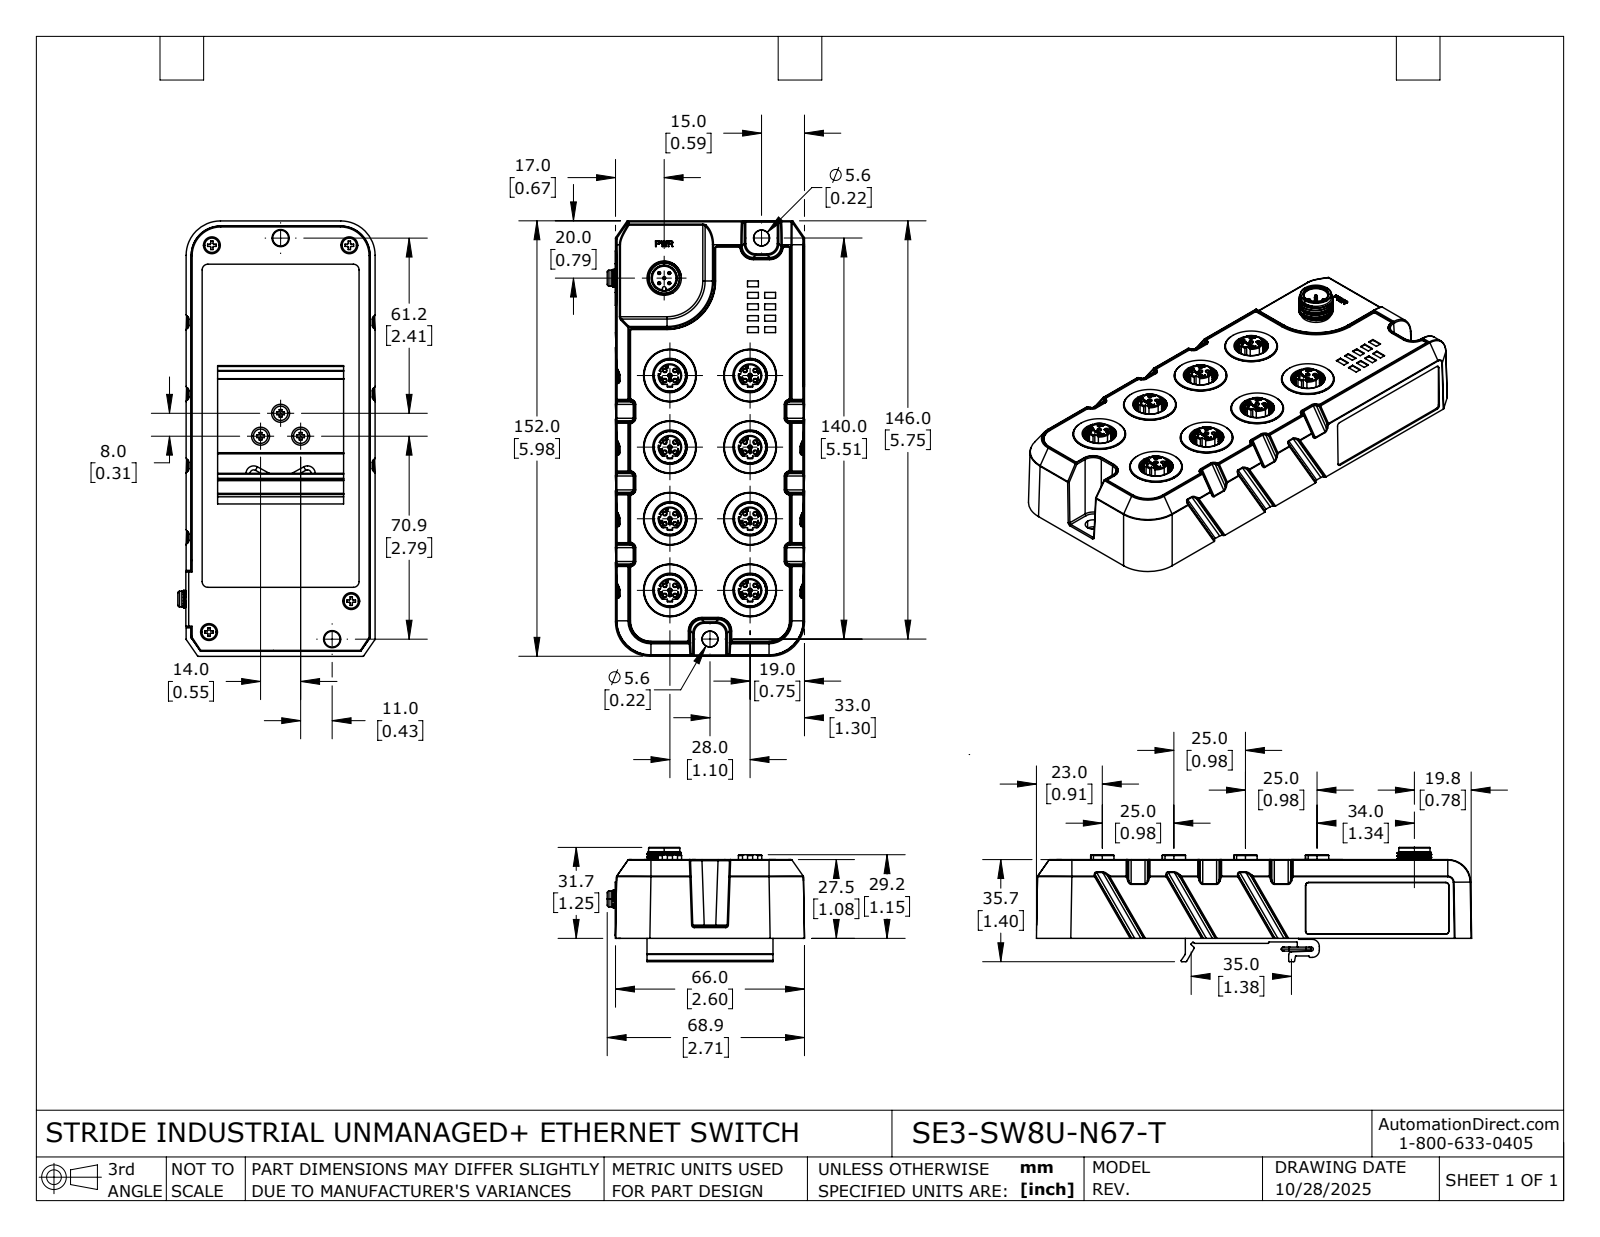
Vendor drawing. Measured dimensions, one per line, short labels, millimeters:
name: SE3-SW8U-N67-T
written by: SolidWorks 2024 (AUTOMOTIVE_DESIGN)
unit: mm
bodies: 9 solids, 4178 faces (2322 planar, 1111 cylindrical, 745 other)
size: 152 × 68.9 × 31.75
volume: 232 624 mm³; area: 78 584 mm²
holes: 40× ⌀1.13, 8× ⌀11, 8× ⌀11.1, 8× ⌀18.2, 4× ⌀4, 2× ⌀6, 1× ⌀2.5, 1× ⌀3.5, 1× ⌀8.3, 1× ⌀8.85, 1× ⌀9.65
bosses: 8× ⌀18.42, 8× ⌀8.15, 5× ⌀1, 4× ⌀5, 1× ⌀10.9, 1× ⌀10.5, 1× ⌀9.3, 1× ⌀5.5
rounds: 182× R0.25, 113× R0.5, 87× R0.4, 43× R1, 39× R0.1, 36× R0.74, 16× R4, 10× R2
face distances: 3, 4.5, 0.5, 26.6, 22.1, 2.75, 22.6, 23.85, 1.75, 27.1
hole spacings: 2.5, 3.54, 25, 23.3, 26.83, 37.54, 25.25, 28
